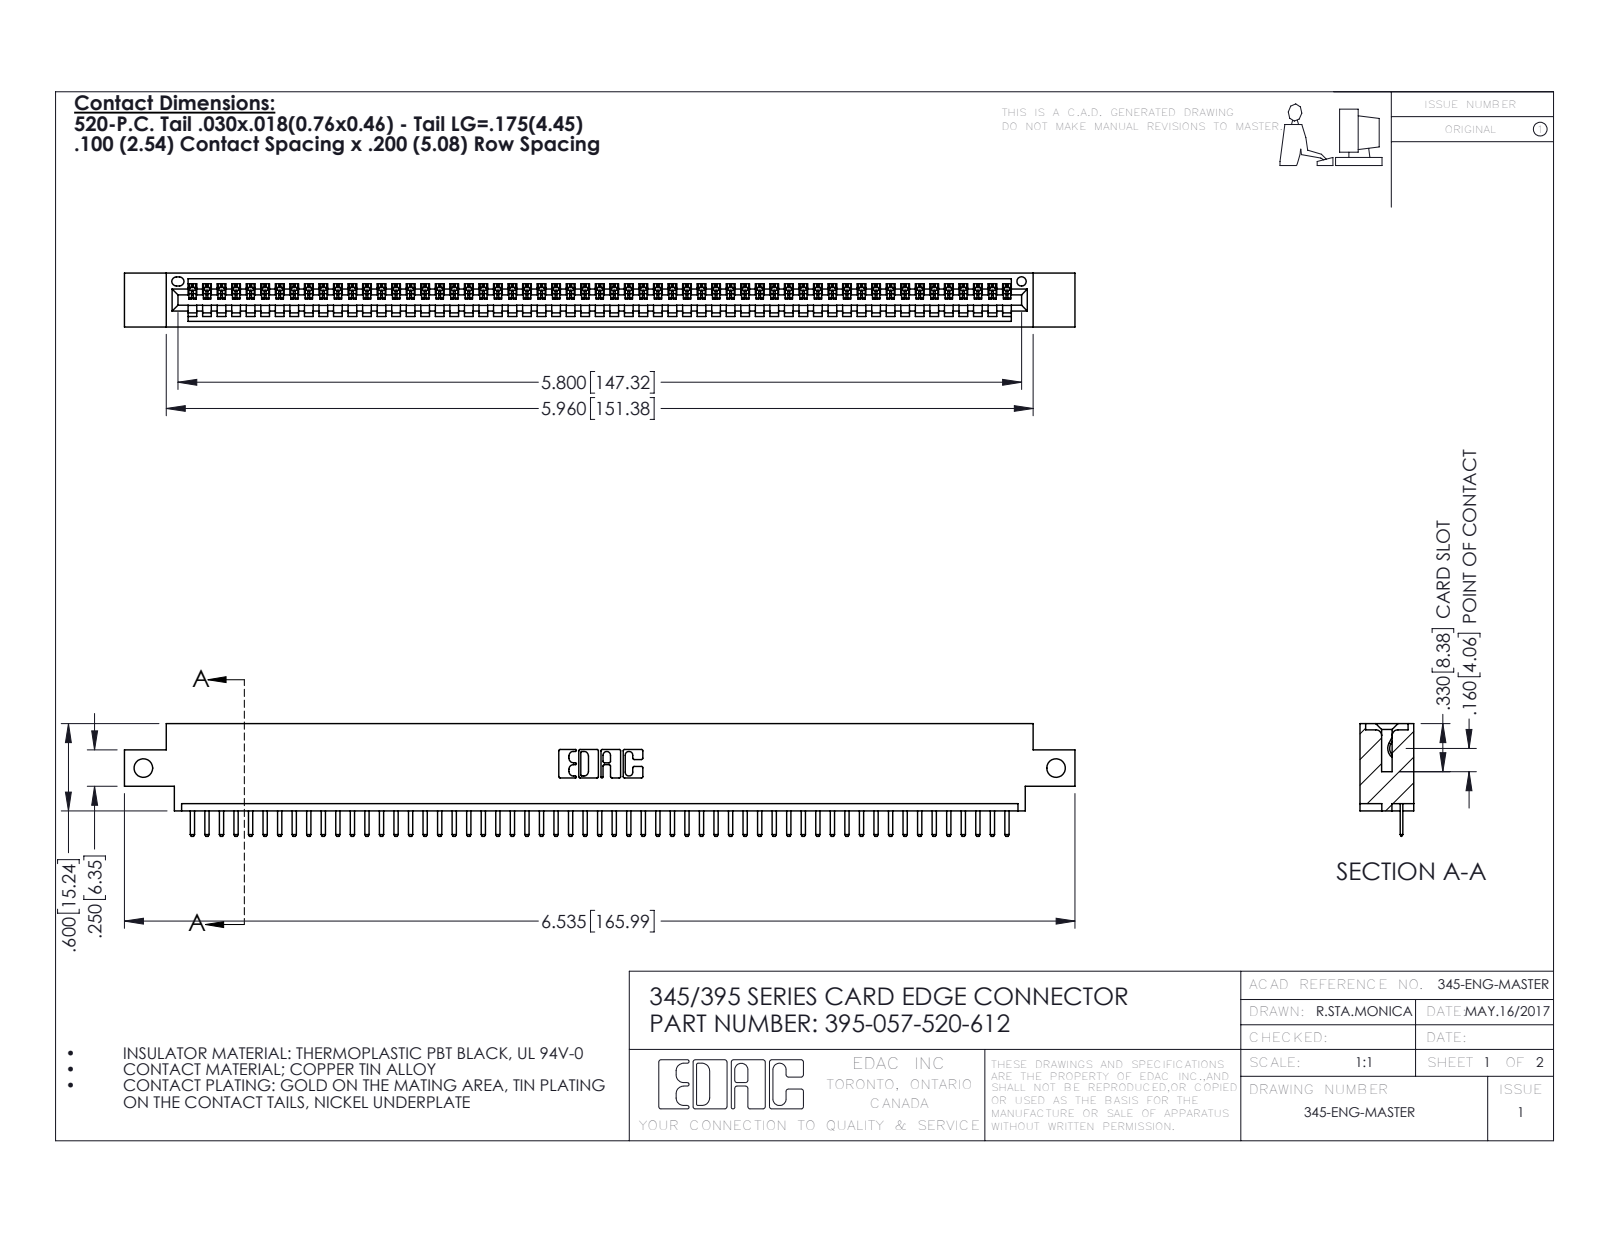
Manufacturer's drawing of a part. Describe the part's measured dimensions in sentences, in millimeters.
The part is named "345 Part_0.170 Offset - Side Mount; 345-292-001_345-293-120; 395-057-520-612". Its 3-D file was written by "SolidWorks 2016 (CONFIG_CONTROL_DESIGN)". It is 58 solids with 3664 faces: 2478 planar, 1186 cylindrical and 0 other. Overall it measures 166 by 19.7 by 9.4 millimeters. Its volume is 15 500 cubic millimeters and its surface area 20 280 square millimeters. Round holes: 2 of diameter 3.3, 1 of diameter 1.6. Partial cylindrical surfaces (rounded edges, fillets, slot ends): 116 of radius 0.3, 114 of radius 0.2, 22 of radius 0.3, 6 of radius 0.2, 6 of radius 0.8, 3 of radius 0.7, 2 of radius 0.8, 2 of radius 1. The main face-to-face distances are 7.6, 1.8, 9.4, 5.1, 2.5, 6.9, 0.6, 5.7, 1.8, 4.4. The hole center spacings are 159.4.
